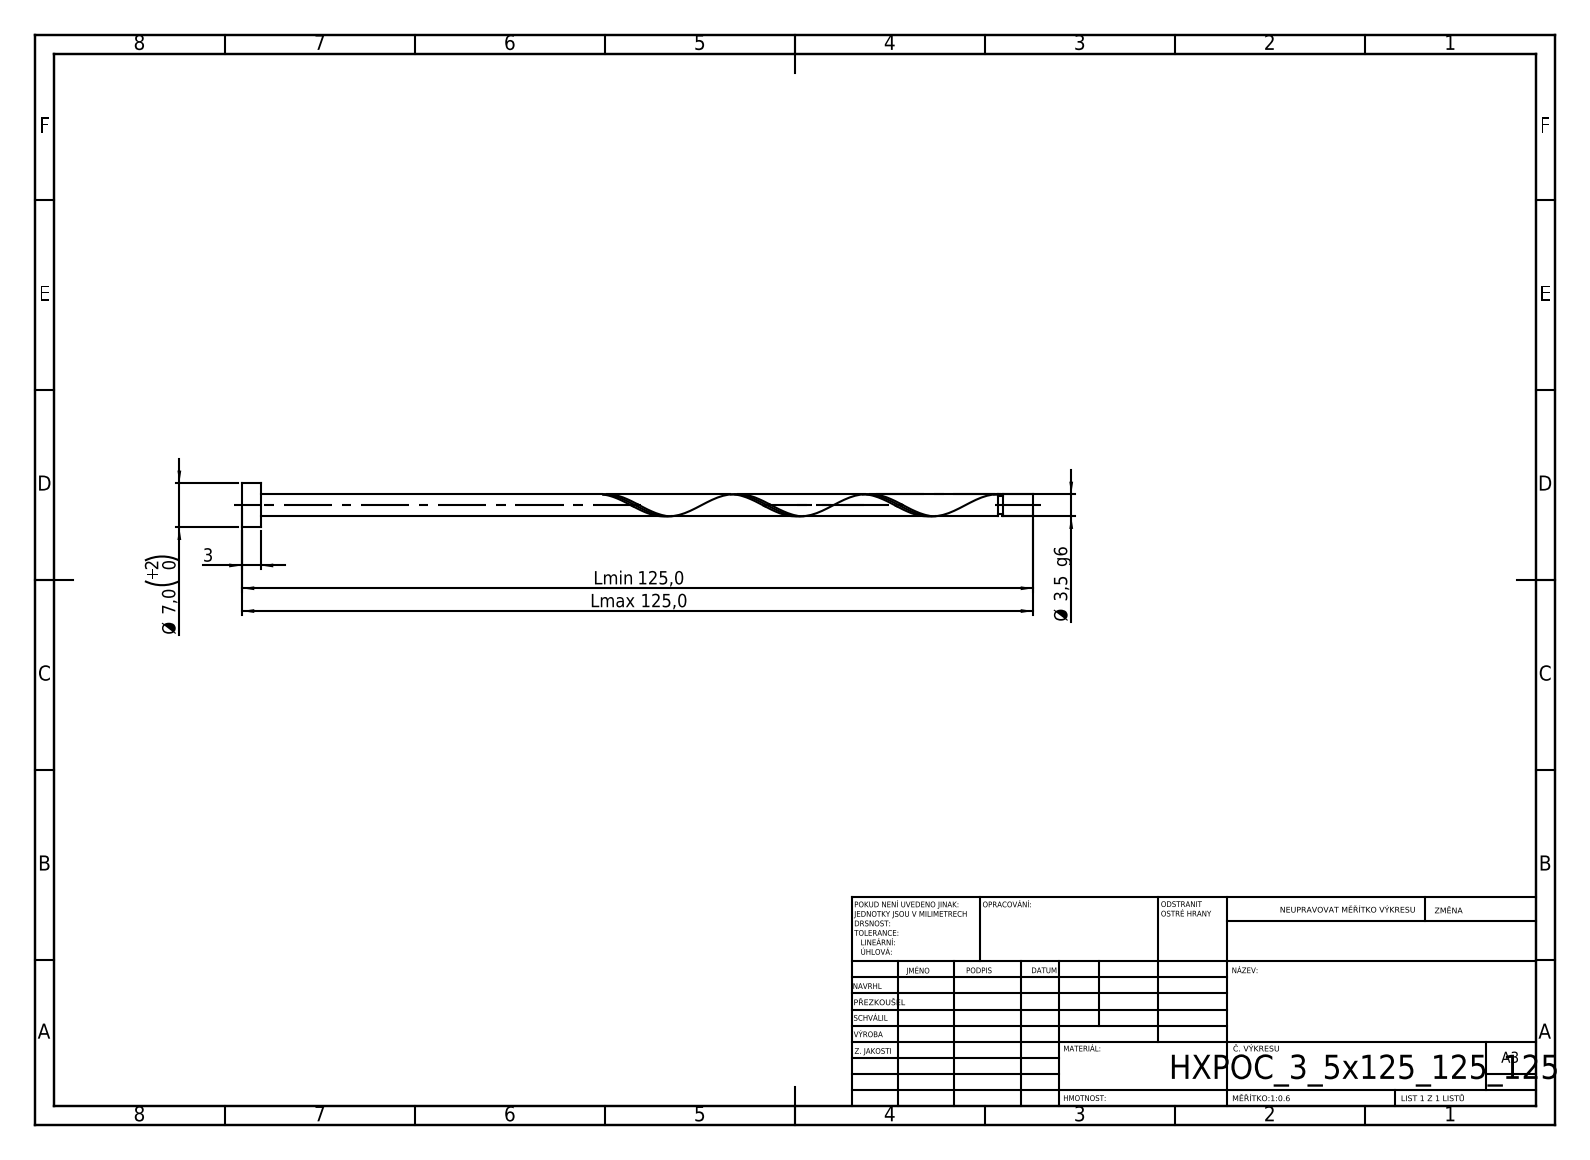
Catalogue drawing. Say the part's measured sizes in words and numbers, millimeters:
Its 3-D file was written by "SolidWorks 2019 (CONFIG_CONTROL_DESIGN)". It is 1 solid with 21 faces: 6 planar, 14 cylindrical and 1 other. Overall it measures 125 by 7 by 7 millimeters. Its volume is 1 275 cubic millimeters and its surface area 1 514 square millimeters. Round bosses or shafts: 1 of diameter 7, 1 of diameter 3.5, 1 of diameter 2.8. The main face-to-face distances are 3, 125, 122, 120.15, 117.15, 4.85, 119.45, 116.45, 0.7, 5.55.
